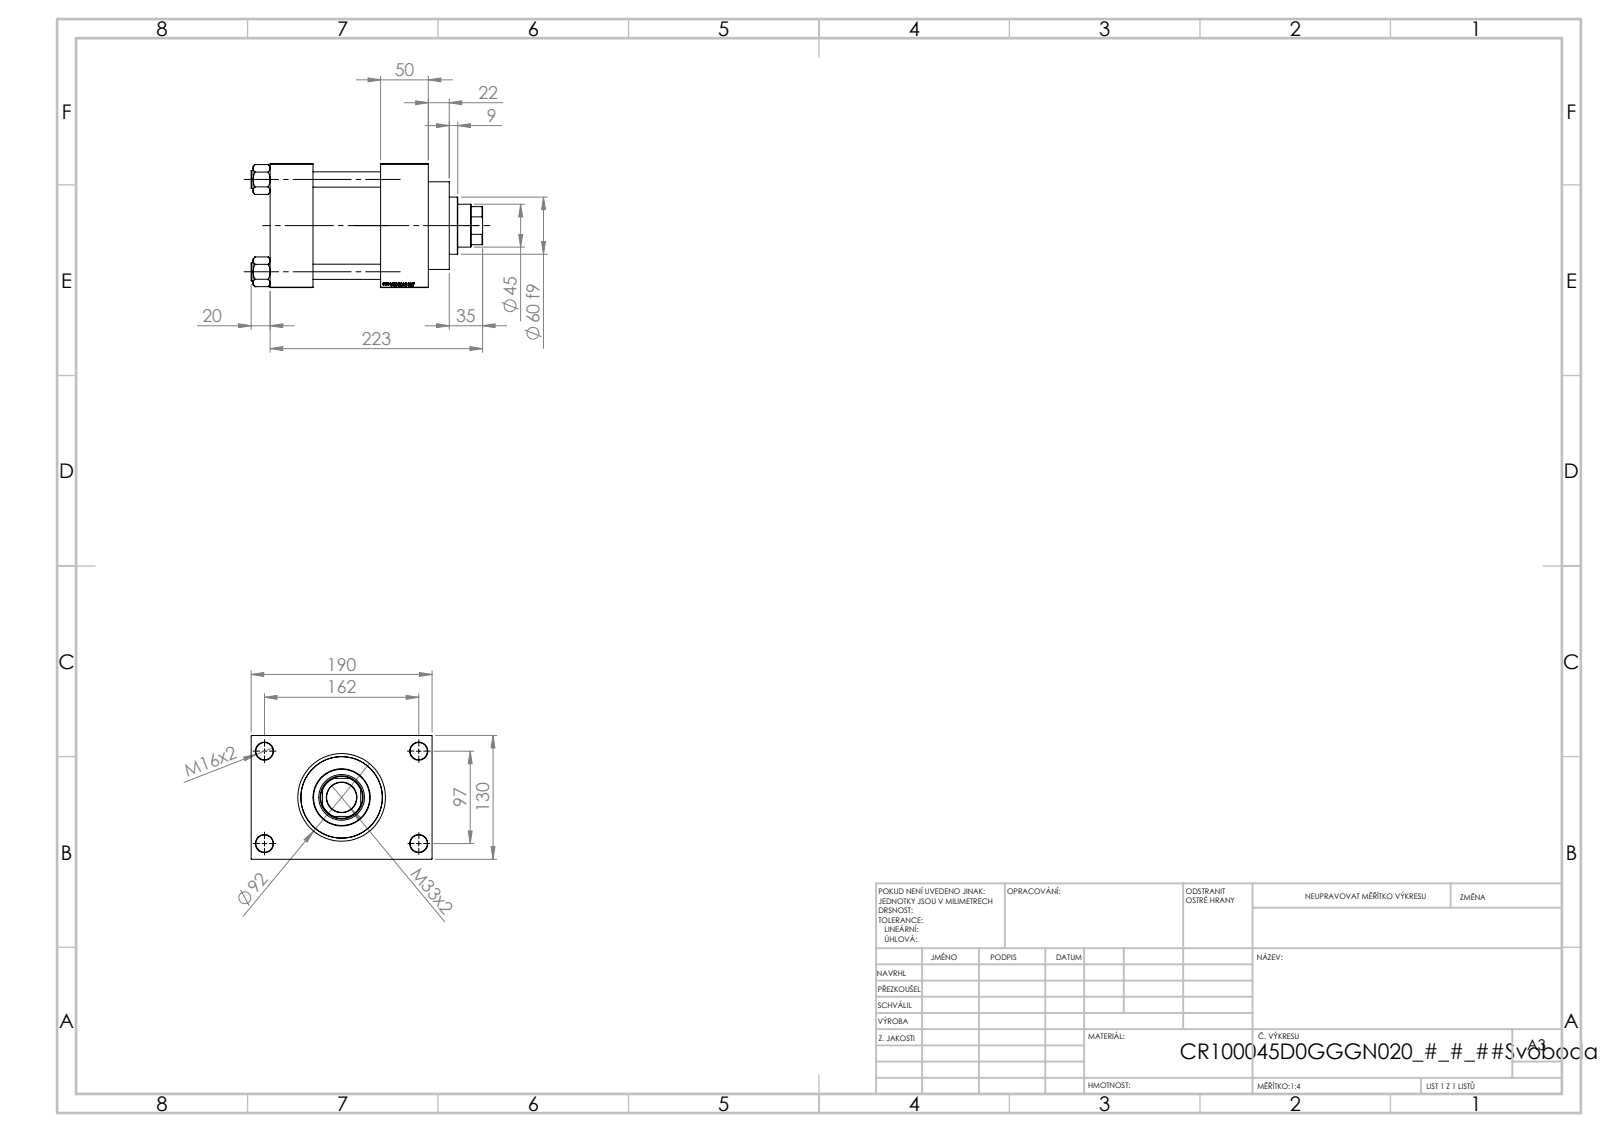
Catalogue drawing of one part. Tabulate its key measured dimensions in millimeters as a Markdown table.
| quantity | value |
| --- | --- |
| part name | V215CR_D_TYCINKA; V215CR_D_Body; V215CR_VCP_D; V215_VC_A (+1 more) |
| STEP written by | SolidWorks 2019 (CONFIG_CONTROL_DESIGN) |
| units | millimeters |
| bodies | 11 solids, 1152 faces (545 planar, 89 cylindrical, 518 other) |
| overall size | 243 × 190 × 130 |
| volume | 2 607 000 mm³ |
| surface area | 352 394 mm² |
| round holes (diameter × count) | 16 × 4, 18 × 4, 7 × 2, 26.44 × 2, 35 × 2, 31.5 × 1, 45 × 1, 48 × 1, 76 × 1, 85.5 × 1, 100 × 1 |
| round bosses / shafts (diameter × count) | 19 × 4, 106 × 1, 92 × 1, 60 × 1 |
| partial cylindrical surfaces (radius × count) | 22 × 1 |
| main face-to-face distances | 130, 45, 116, 71, 166, 121, 50, 30, 160, 20 |
| hole center spacings | 32.55, 68.52, 94.41, 96.9, 102.27, 129.45, 161.73, 97 |
